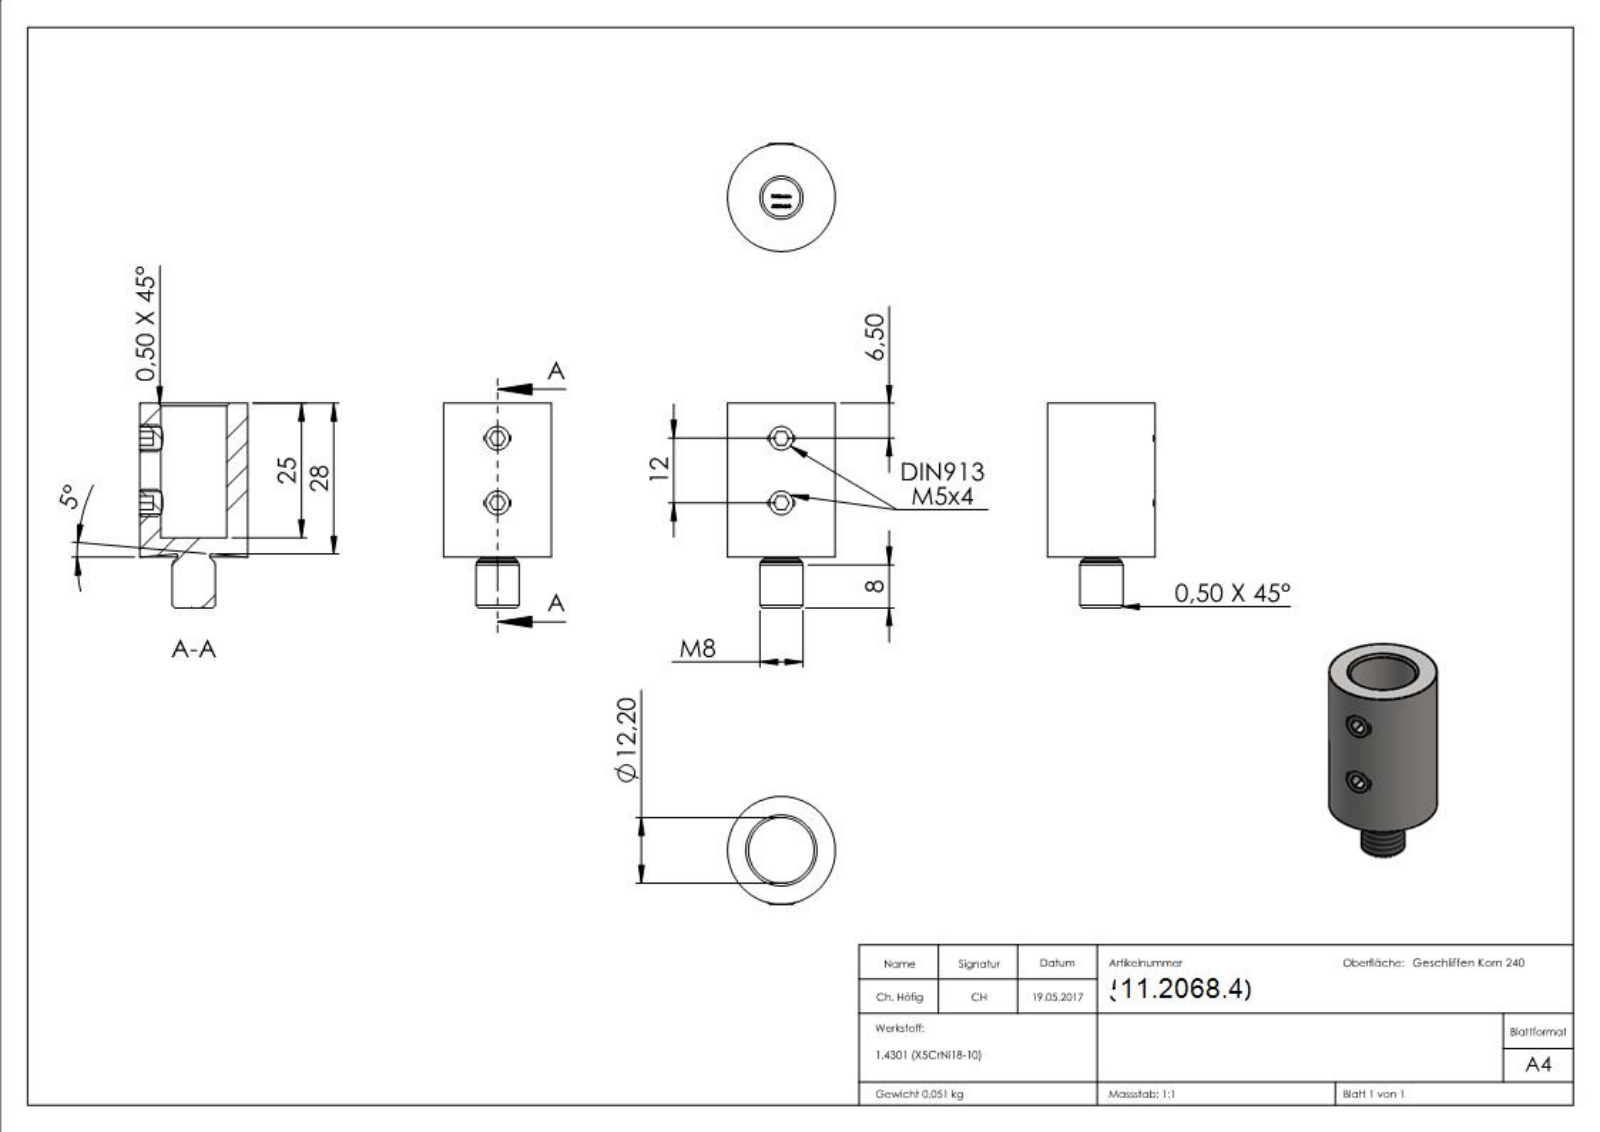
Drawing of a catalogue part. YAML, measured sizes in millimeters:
part_name: "DIN913 M5x4_DIN913 M5x6; 50390-240; DIN913 M5x4; 50390-240 Teil1"
step_written_by: "SolidWorks 2018 (CONFIG_CONTROL_DESIGN)"
units: millimeters
bodies: {solids: 3, faces: 336, planar: 135, cylindrical: 44, other: 157}
overall_size: [11800, 5000, 5000]
volume: 6427
surface_area: 3962
round_holes:
  - {diameter: 4.2, count: 2}
  - {diameter: 12.2, count: 1}
round_bosses_or_shafts:
  - {diameter: 5, count: 2}
  - {diameter: 20, count: 1}
  - {diameter: 8, count: 1}
  - {diameter: 6, count: 1}
partial_cylinders:
  - {radius: 0.1, count: 36}
face_to_face_distances: [25, 13, 38, 2.5, 4, 6, 1.5, 7.75, 8.5, 3.5]
hole_center_spacings: [12]
